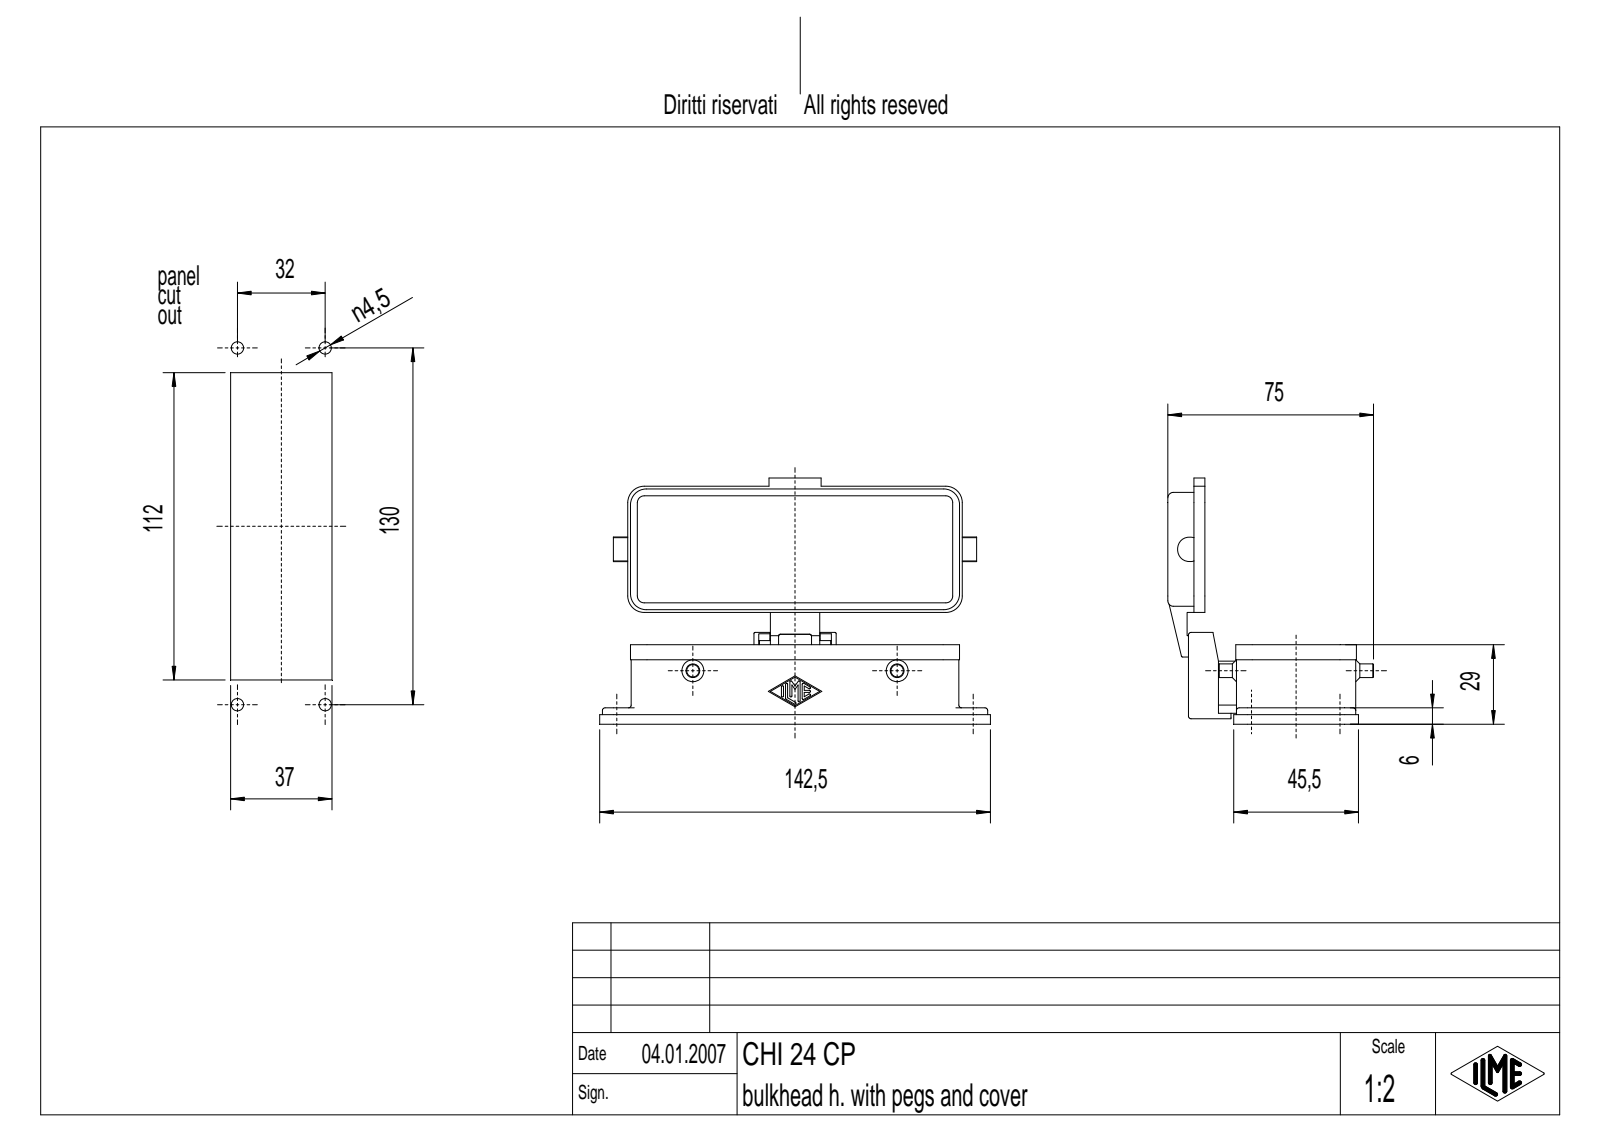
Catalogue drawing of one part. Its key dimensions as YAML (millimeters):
part_name: "CHI 24 CP"
step_written_by: "Autodesk Inventor 7 (AUTOMOTIVE_DESIGN)"
units: millimeters
bodies: {solids: 1, faces: 470, planar: 205, cylindrical: 179, other: 86}
overall_size: [142.5, 89.75, 75]
volume: 65629
surface_area: 49694
round_holes:
  - {diameter: 4.5, count: 4}
  - {diameter: 4.6, count: 4}
  - {diameter: 4, count: 1}
  - {diameter: 5, count: 1}
round_bosses_or_shafts:
  - {diameter: 5, count: 2}
  - {diameter: 3, count: 2}
  - {diameter: 7, count: 1}
  - {diameter: 4, count: 1}
partial_cylinders:
  - {radius: 0.38, count: 14}
  - {radius: 6, count: 12}
  - {radius: 0.5, count: 10}
  - {radius: 0.7, count: 8}
  - {radius: 1, count: 8}
  - {radius: 2, count: 8}
  - {radius: 2.5, count: 8}
  - {radius: 3, count: 4}
face_to_face_distances: [2.5, 3, 40.5, 4, 40.75, 1.25, 0.75, 1, 25.5, 43.75]
hole_center_spacings: [32, 130, 133.88]
